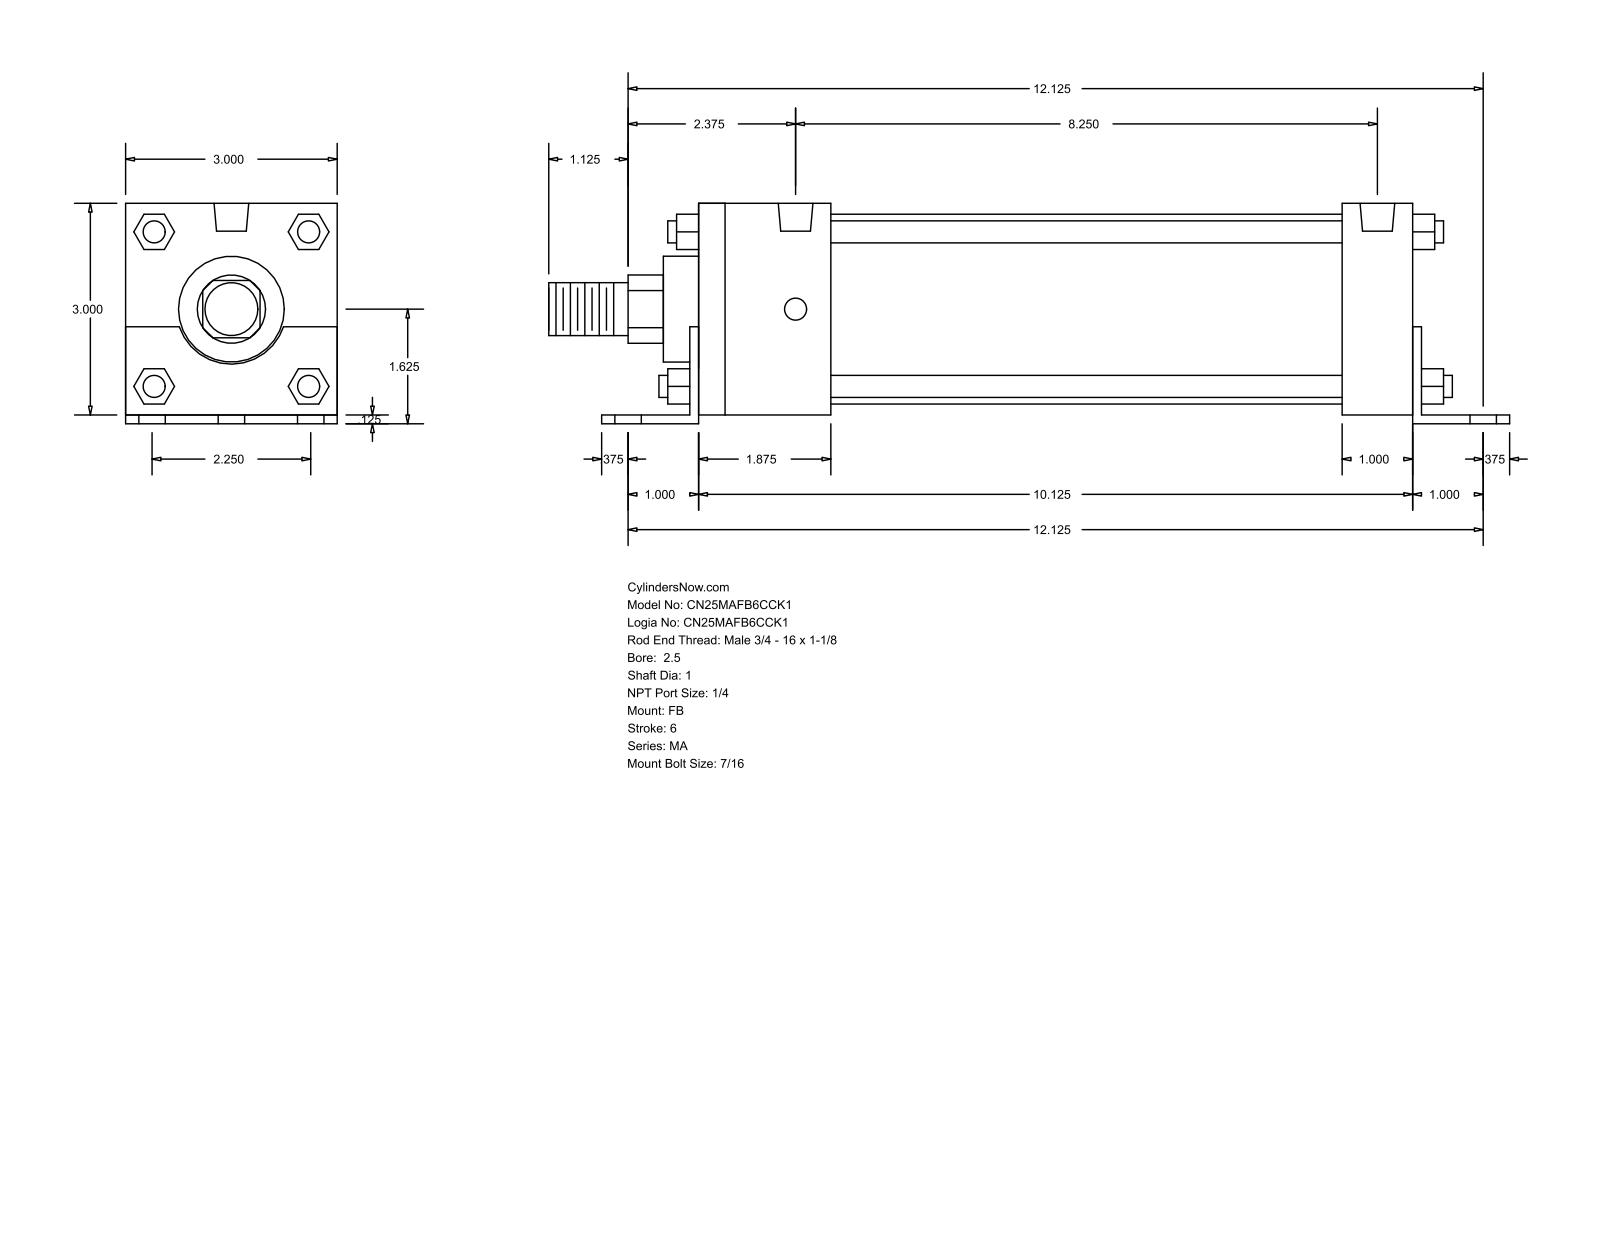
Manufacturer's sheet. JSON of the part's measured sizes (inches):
{"part_name": "MA_FB__0250_1", "step_written_by": "GSSL Pune (CONFIG_CONTROL_DESIGN)", "units": "inches", "bodies": {"solids": 0, "faces": 140, "planar": 105, "cylindrical": 35, "other": 0}, "overall_size": [13.625, 3.125, 3], "round_holes": [[0.437, 6], [0.313, 4], [0.492, 2]], "round_bosses_or_shafts": [[0.313, 4], [2.69, 1], [1.5, 1], [1, 1], [0.75, 1]], "partial_cylinders_radius": [[0.484, 1], [0.78, 1]], "face_to_face_distances": [3, 0.125, 3.125, 10.125, 0.125, 0.5, 10.25, 1.125, 2, 1.875], "hole_center_spacings": [1.125, 12.177, 12.125, 1.875, 2.25, 2.628, 8.25, 9.815]}
